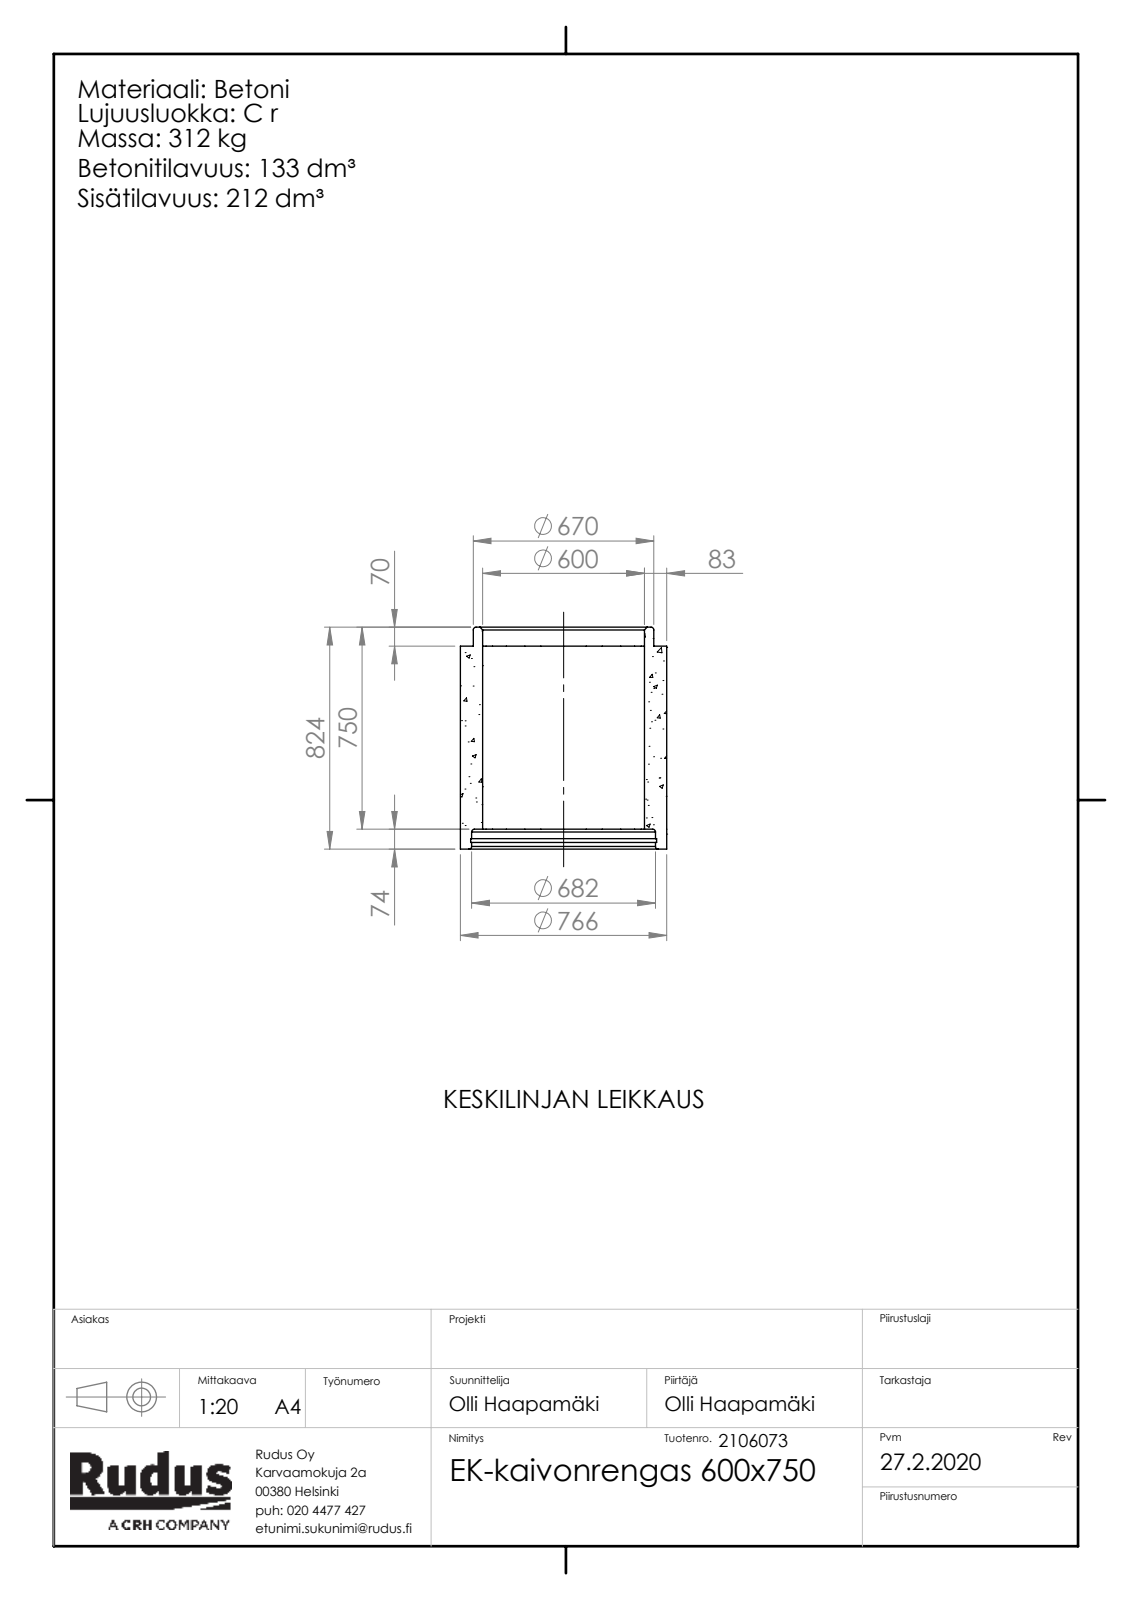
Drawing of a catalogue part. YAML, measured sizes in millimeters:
part_name: "Rudus 2106073 EK-kaivonrengas 600x750; EK-osa-kaivorunko_EK-kaivonrengas"
step_written_by: "SolidWorks 2019 (CONFIG_CONTROL_DESIGN)"
units: millimeters
bodies: {solids: 1, faces: 107, planar: 7, cylindrical: 12, other: 88}
overall_size: [824, 766, 766]
volume: 132800000
surface_area: 3874000
round_holes:
  - {diameter: 600, count: 1}
  - {diameter: 682, count: 1}
  - {diameter: 690, count: 1}
round_bosses_or_shafts:
  - {diameter: 766, count: 1}
  - {diameter: 670, count: 1}
face_to_face_distances: [754, 74, 680, 824, 750, 70, 25, 49, 729, 799]
